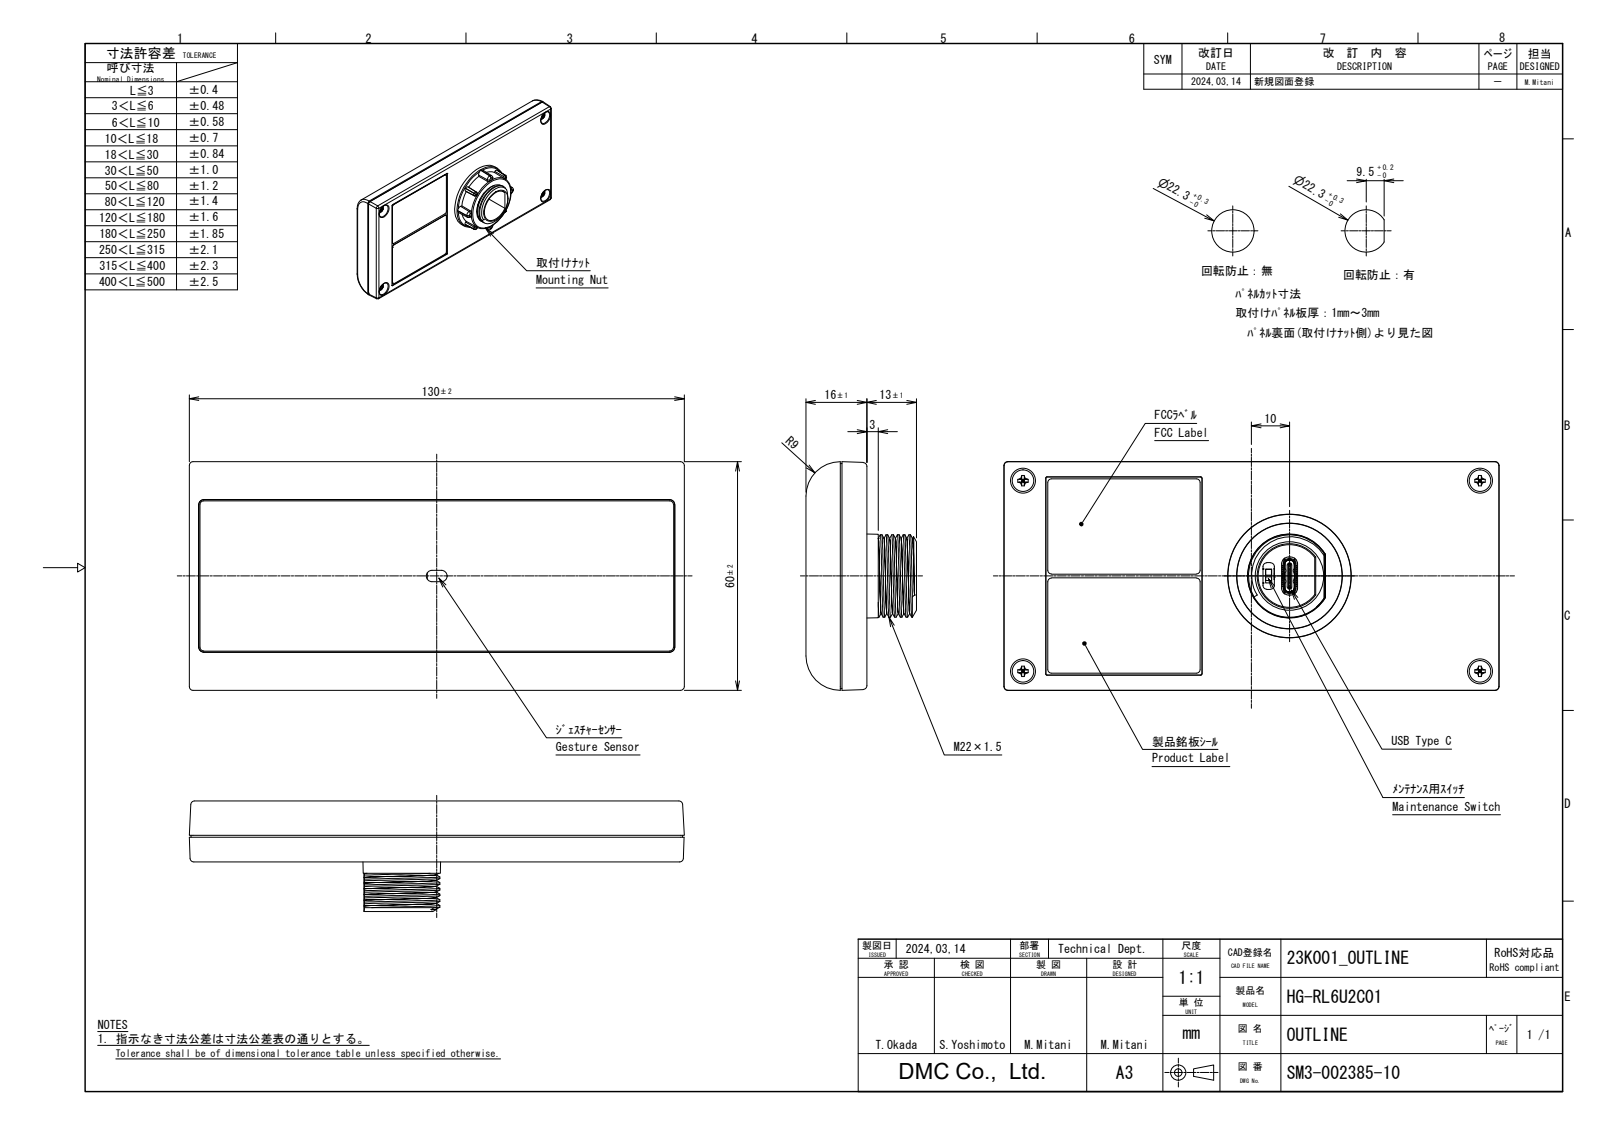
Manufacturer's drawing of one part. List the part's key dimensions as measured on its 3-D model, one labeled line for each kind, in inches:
STEP written by: Autodesk Inventor 2020 (CONFIG_CONTROL_DESIGN)
Units: inches
Bodies: 1 solid, 5442 faces (3673 planar, 1259 cylindrical, 510 other)
Overall size (bounding box): 5.118 × 2.362 × 1.142
Volume: 4.065 in³ · Surface area: 106.5 in²
Round holes (diameter × count): ⌀0.039 ×6, ⌀0.138 ×6, ⌀0.118 ×5, ⌀0.102 ×4, ⌀0.031 ×1, ⌀0.879 ×1, ⌀1.102 ×1
Round bosses / shafts (diameter × count): ⌀0.118 ×4, ⌀0.014 ×4, ⌀0.031 ×2, ⌀0.02 ×2, ⌀1.26 ×1, ⌀0.85 ×1, ⌀0.039 ×1, ⌀0.024 ×1
Partial cylindrical surfaces — rounded edges, fillets, slot ends (radius × count): R0.004 ×161, R0.008 ×51, R0.039 ×50, R0.012 ×38, R0.006 ×28, R0.016 ×26, R0.02 ×20, R0.028 ×11
Main face-to-face distances: 0.098, 0.522, 0.62, 0.457, 0.359, 0.163, 0.091, 0.45, 0.063, 0.1
Hole centre spacings: 0.394, 0.472, 1.016, 1.285, 1.427, 1.575, 1.63, 1.867
